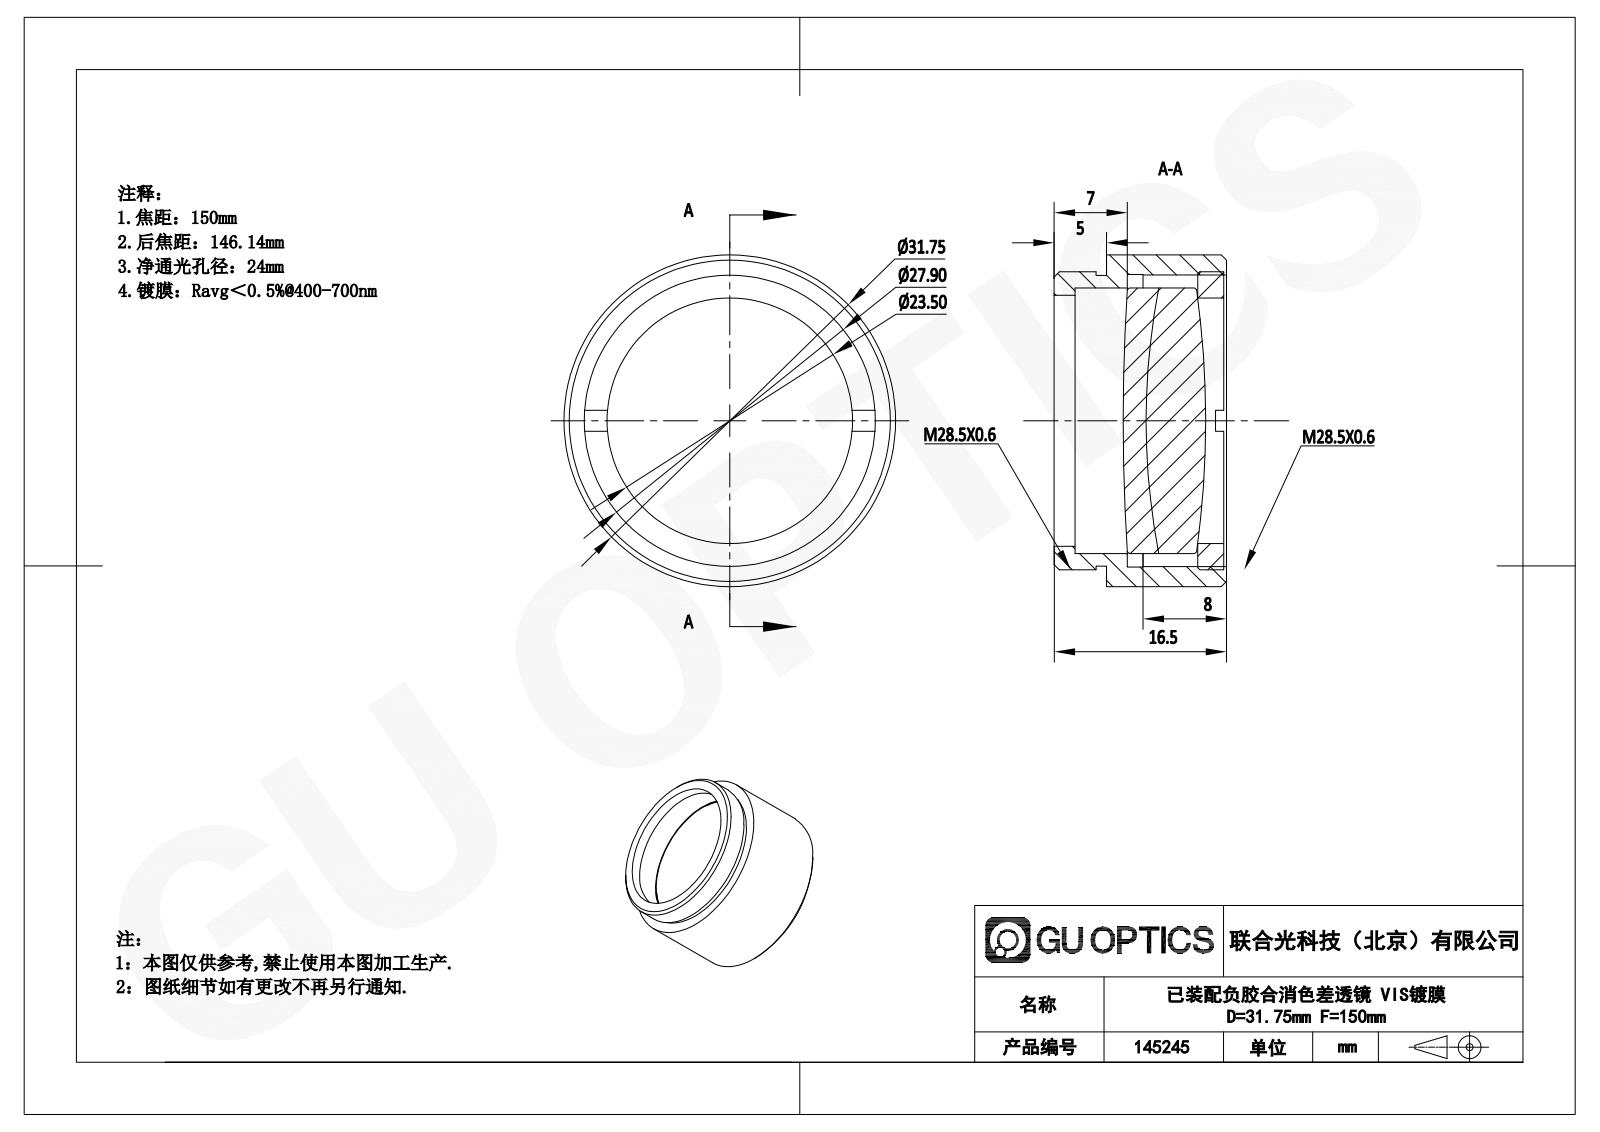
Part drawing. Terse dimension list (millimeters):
name: M28.5x0.6ѹȦ; GL31-025B-150-VIS_Solidworks; APD-ML25-150-VIS
written by: SolidWorks 2022 (AUTOMOTIVE_DESIGN)
unit: mm
bodies: 4 solids, 56 faces (16 planar, 22 cylindrical, 18 other)
size: 31.76 × 31.76 × 16.5
volume: 7 162 mm³; area: 7 028 mm²
holes: 1× ⌀23.5, 1× ⌀24, 1× ⌀27.9, 1× ⌀28
bosses: 1× ⌀31.76, 1× ⌀28.5, 1× ⌀27.8, 1× ⌀25.4
face distances: 2, 5, 2.5, 8.74, 11.24, 13.74, 16.24, 16.5, 11.5, 2.76
